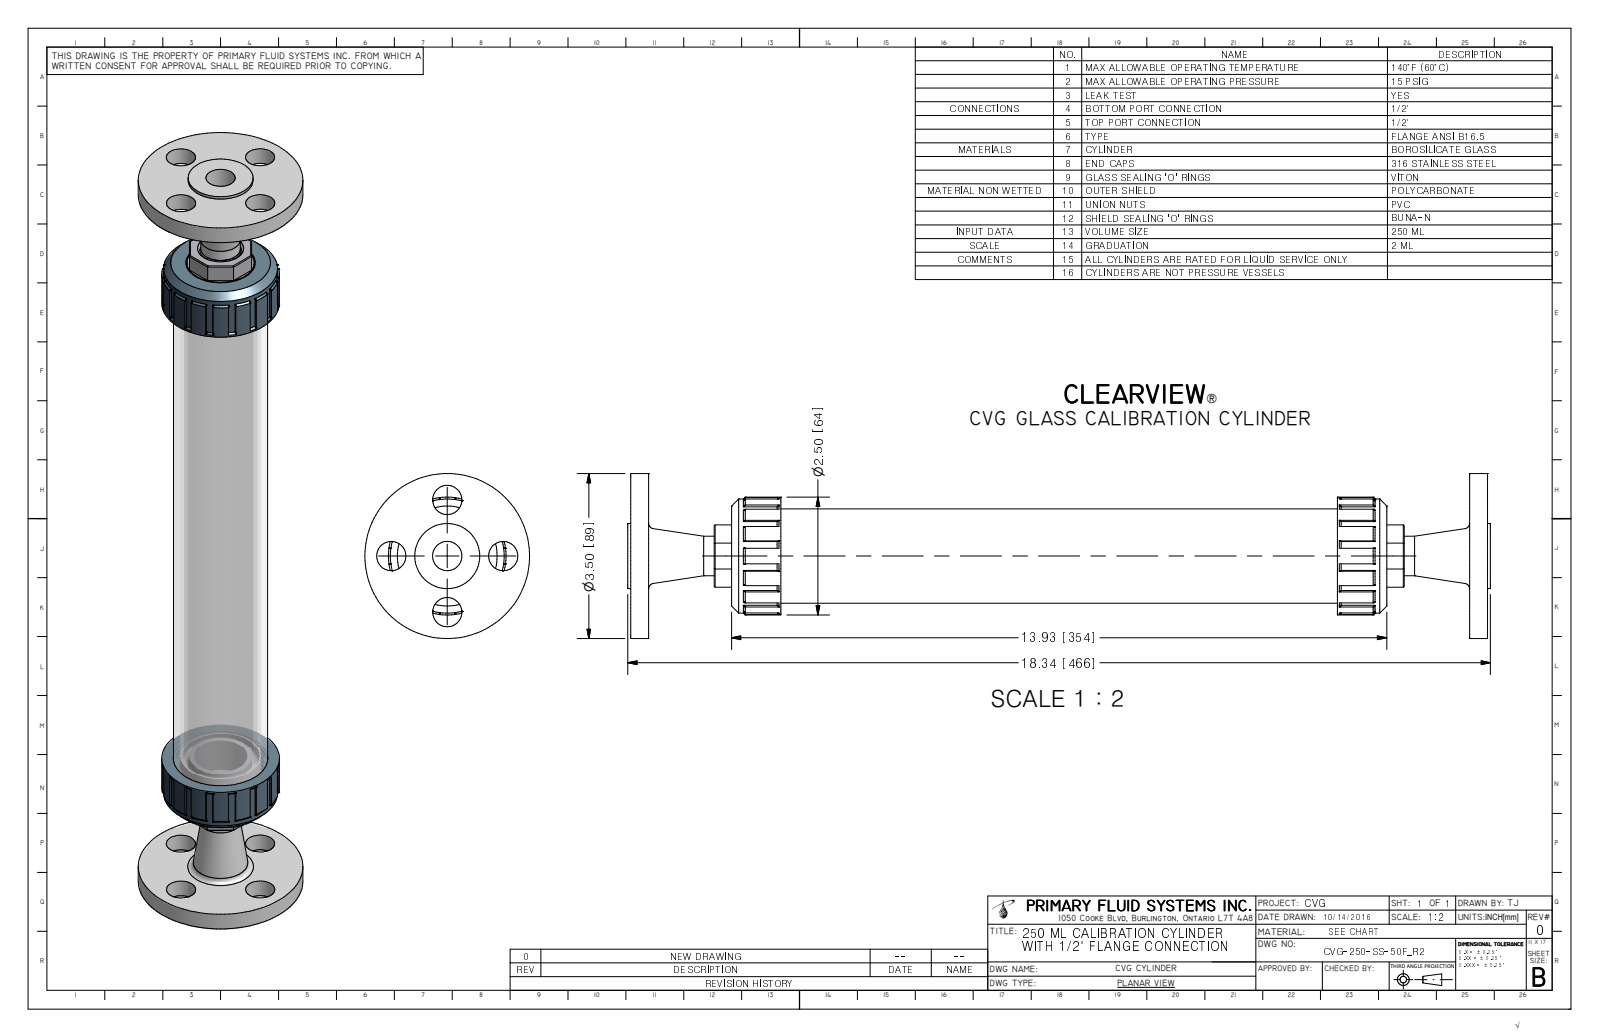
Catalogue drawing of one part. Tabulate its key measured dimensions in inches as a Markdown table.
| quantity | value |
| --- | --- |
| part name | CVG-250-SS-50F_R0; CVG-3-250-METAL-S-50_R1; CVG-6-250_R0; CVG-1-250-A_R0 (+2 more) |
| STEP written by | Autodesk Inventor 2009 (AUTOMOTIVE_DESIGN) |
| units | inches |
| bodies | 8 solids, 340 faces (99 planar, 53 cylindrical, 188 other) |
| overall size | 18.34 × 3.5 × 3.5 |
| volume | 28.08 in³ |
| surface area | 413.5 in² |
| round holes (diameter × count) | 0.62 × 4, 0.622 × 1, 0.702 × 1, 0.88 × 1, 1.14 × 1, 1.417 × 1, 1.635 × 1, 1.75 × 1 |
| round bosses / shafts (diameter × count) | 3.5 × 1, 2.5 × 1, 2 × 1, 1.921 × 1, 1.86 × 1, 1.725 × 1, 1.591 × 1, 1.575 × 1 |
| main face-to-face distances | 0.38, 17.835, 18.215, 17.455, 3.193, 15.022, 2.813, 14.643, 0.063, 0.443 |
| hole center spacings | 1.19, 1.683, 2.38 |
